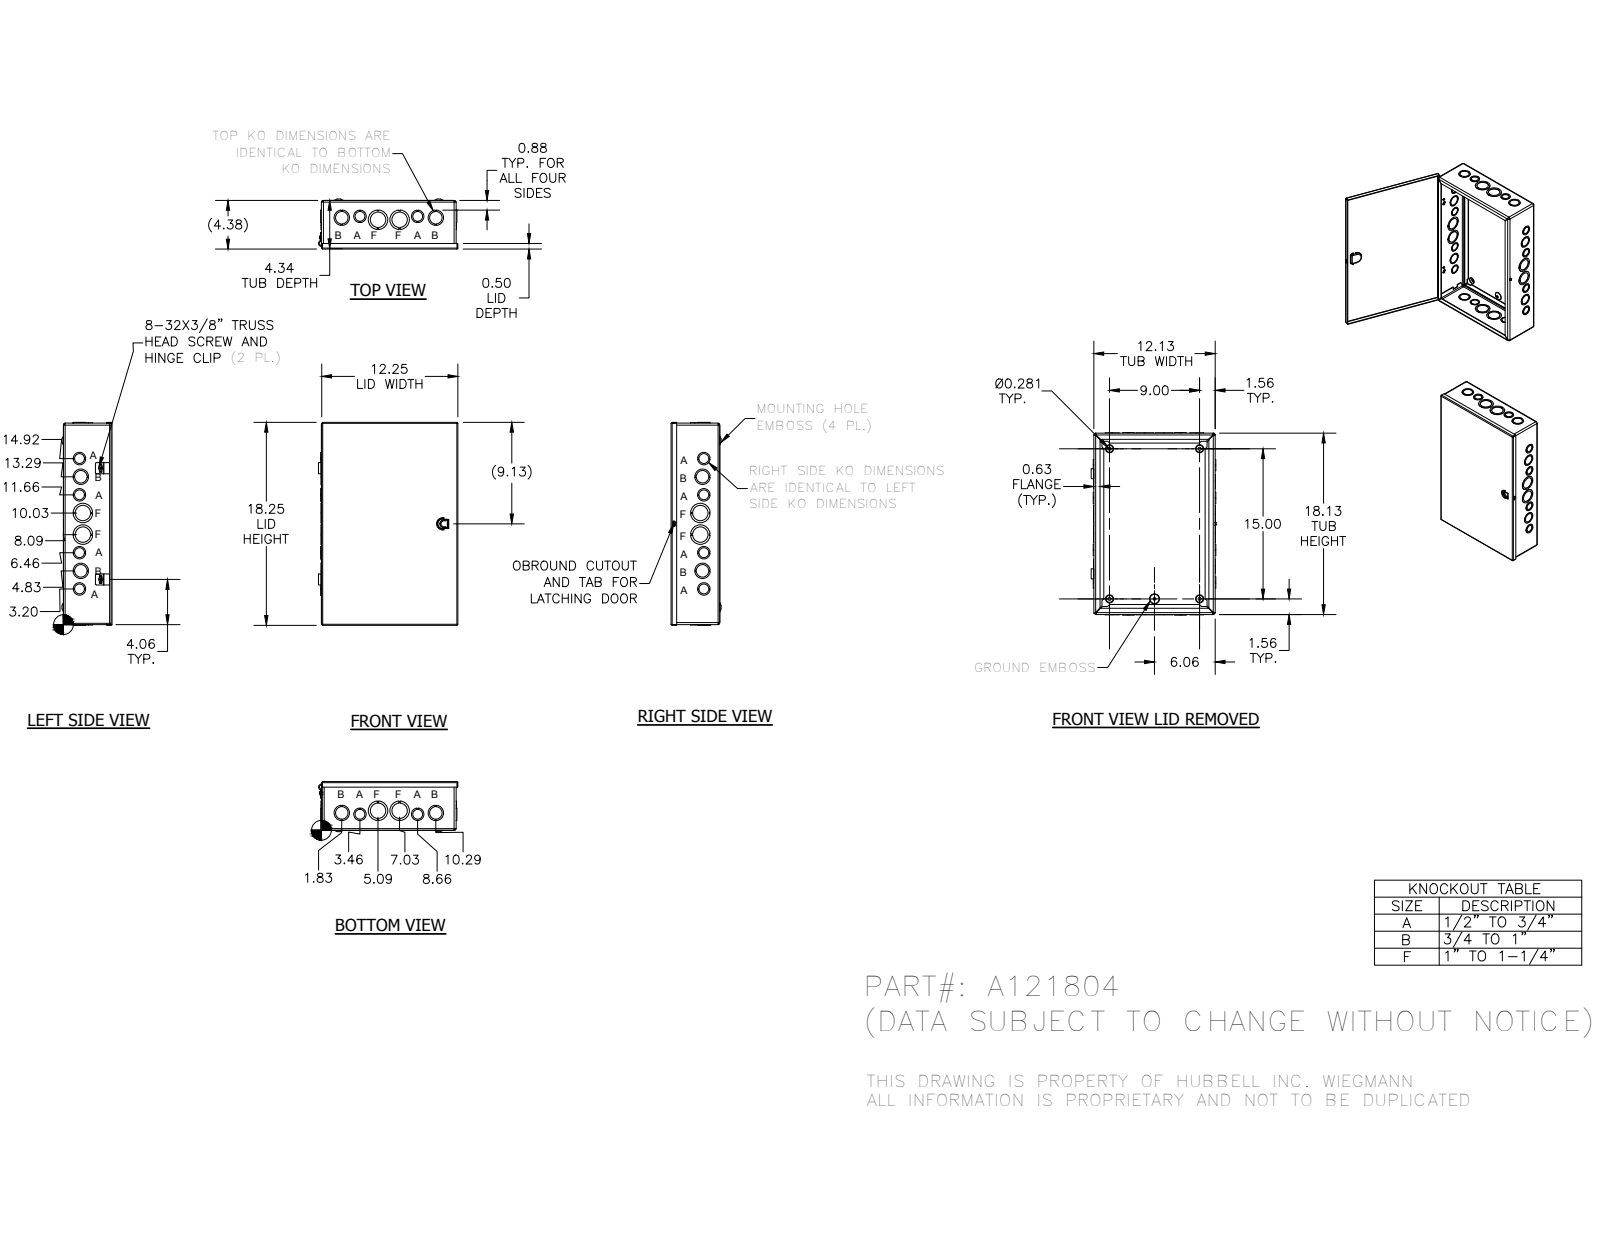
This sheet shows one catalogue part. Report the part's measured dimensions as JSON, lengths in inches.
{"part_name": "A1218BA; A121804WRA; 31816; 372177 (+3 more)", "step_written_by": "Autodesk Inventor 2014 (AUTOMOTIVE_DESIGN)", "units": "inches", "bodies": {"solids": 31, "faces": 1279, "planar": 846, "cylindrical": 275, "other": 158}, "overall_size": [18.437, 12.637, 4.504], "round_holes": [[1.125, 10], [1.375, 8], [0.875, 6], [0.3, 4], [1.75, 4], [0.14, 2], [0.165, 1]], "round_bosses_or_shafts": [[0.384, 2], [0.164, 2], [0.228, 1]], "partial_cylinders_radius": [[0.125, 15], [0.031, 10], [0.063, 9], [0.094, 8], [0.187, 8], [0.055, 4], [0.062, 4], [0.07, 4]], "face_to_face_distances": [0.062, 0.062, 4.316, 4.254, 0.063, 4.317, 4.379, 12.063, 12.125, 12.001], "hole_center_spacings": [1.635, 1.659, 3.265, 3.584, 5.204, 6.831, 8.46, 1.94]}
